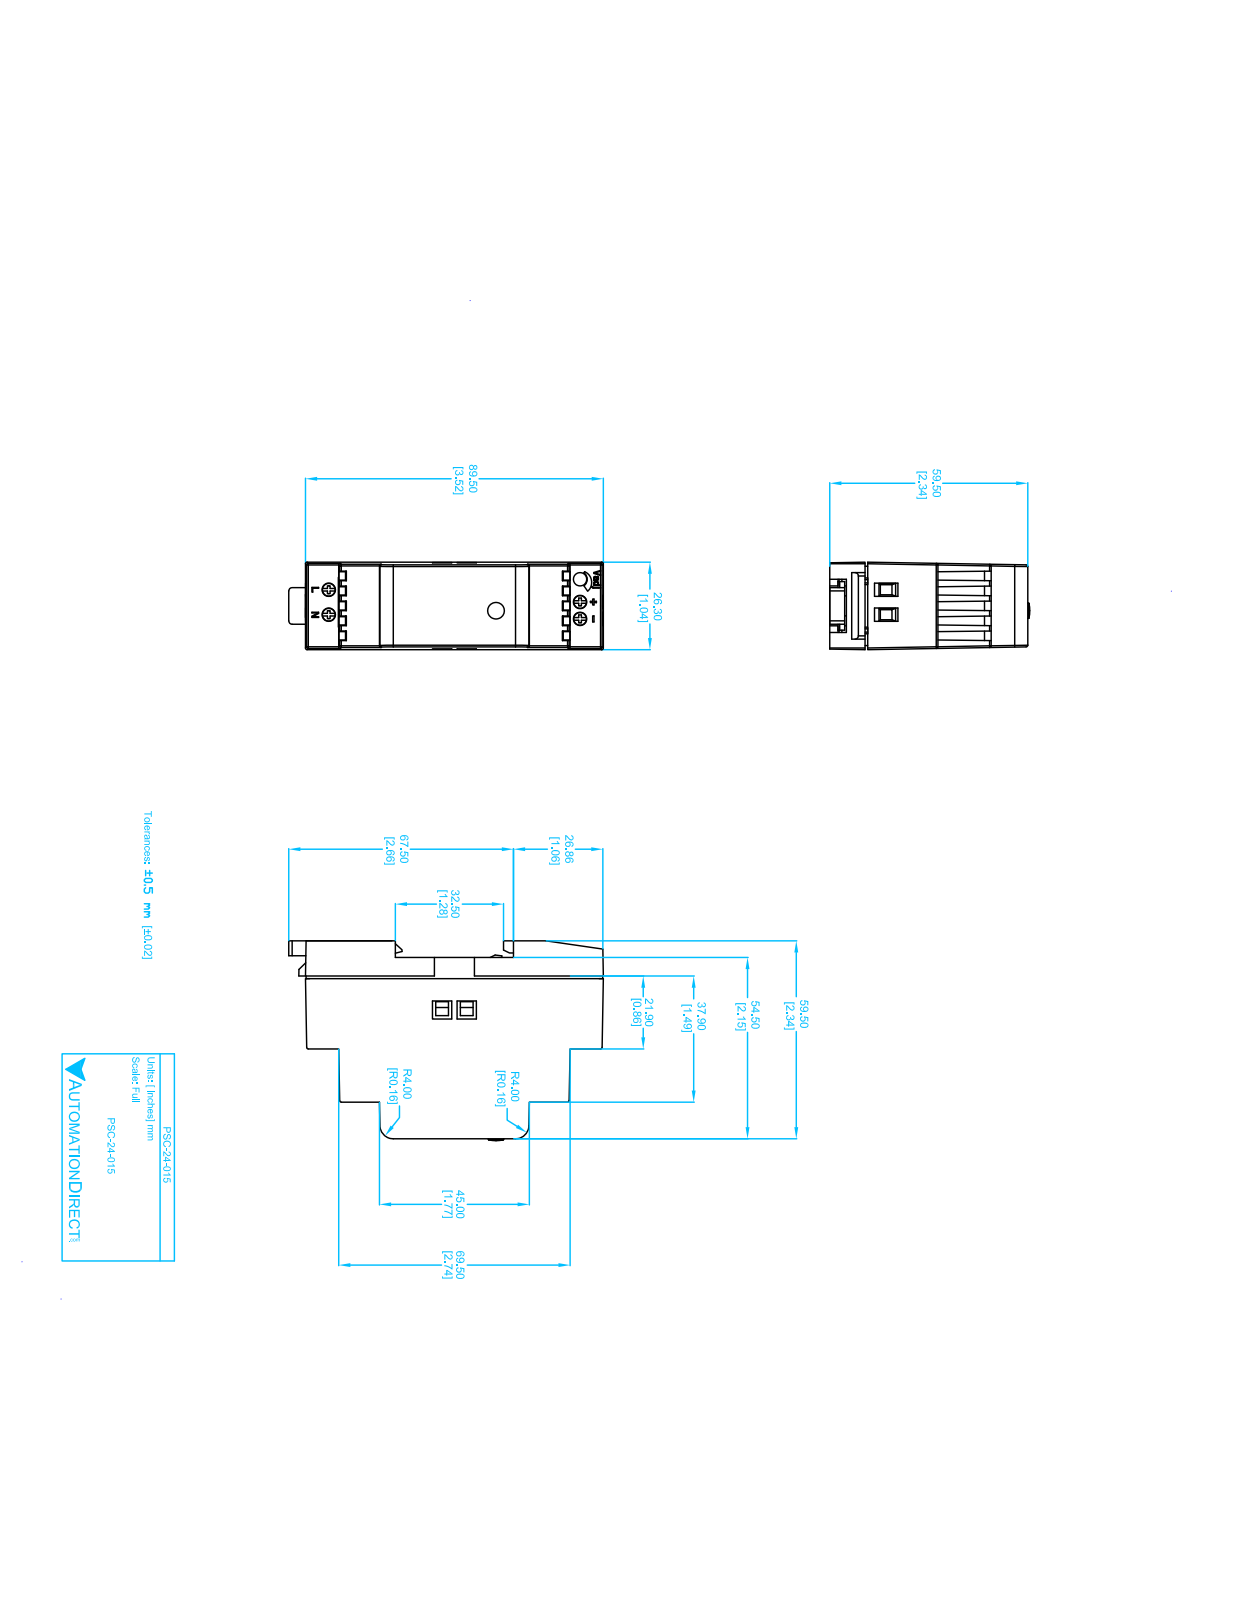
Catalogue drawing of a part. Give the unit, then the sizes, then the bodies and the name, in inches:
Units: inches
Overall size (bounding box): 3.719 × 2.372 × 1.039
Round holes (diameter × count): ⌀0.16 ×5
Round bosses / shafts (diameter × count): ⌀0.2 ×1
Partial cylindrical surfaces — rounded edges, fillets, slot ends (radius × count): R0.02 ×26, R0.04 ×2, R0.16 ×2
Main face-to-face distances: 1.039, 0.19, 0.595, 2.341, 2.151, 1.9, 0.44, 1.71, 0.441, 1.27
Hole centre spacings: 0.2, 0.25, 0.3, 0.45, 3.02, 3.021, 3.025, 3.028
Volume: 6.452 in³ · Surface area: 32.1 in²
Bodies: 1 solid, 441 faces (351 planar, 54 cylindrical, 36 other)
Part name (STEP PRODUCT): PSC-24-015
STEP written by: SolidWorks 2011 (CONFIG_CONTROL_DESIGN)
